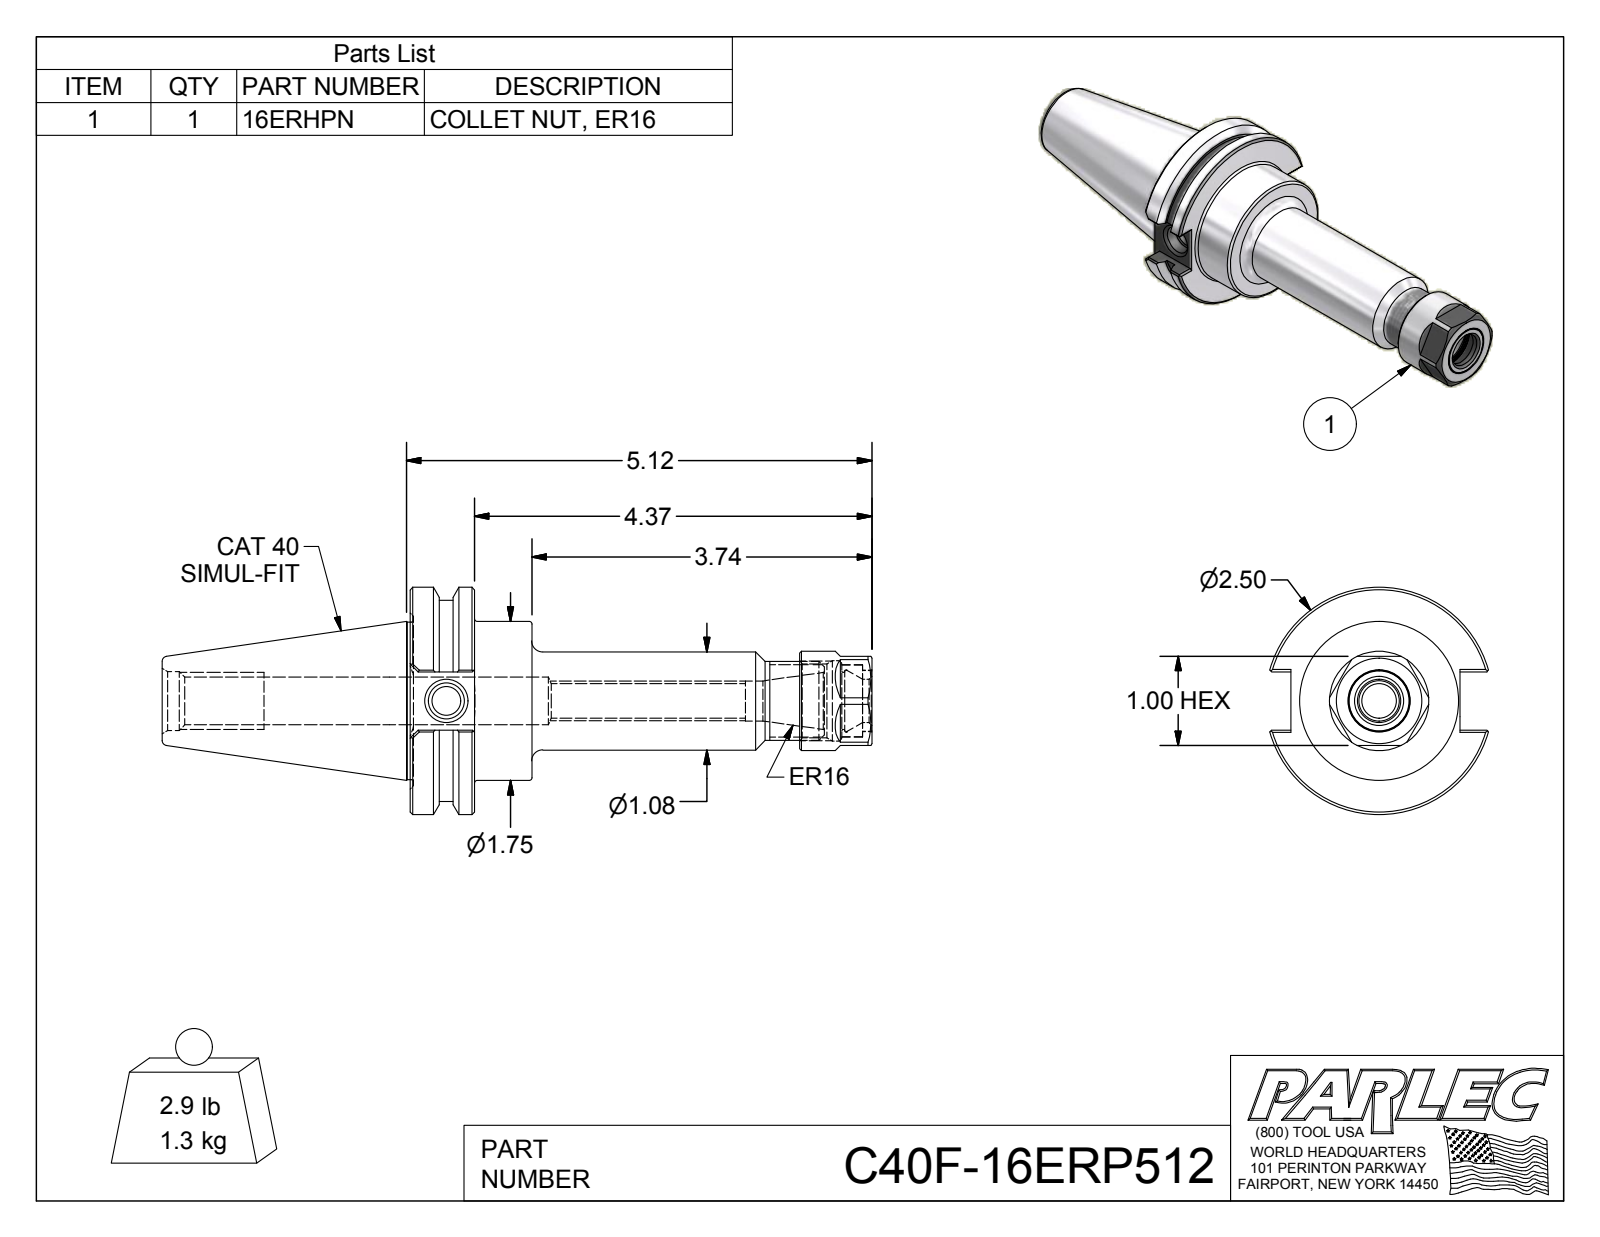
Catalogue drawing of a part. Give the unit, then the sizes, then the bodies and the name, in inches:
Units: inches
Overall size (bounding box): 7.808 × 2.5 × 2.406
Round holes (diameter × count): ⌀0.315 ×1, ⌀0.383 ×1, ⌀0.399 ×1, ⌀0.44 ×1, ⌀0.474 ×1, ⌀0.527 ×1, ⌀0.527 ×1, ⌀0.63 ×1, ⌀0.648 ×1, ⌀0.674 ×1, ⌀0.68 ×1, ⌀0.794 ×1
Round bosses / shafts (diameter × count): ⌀2.5 ×1, ⌀2.215 ×1, ⌀1.75 ×1, ⌀1.73 ×1, ⌀1.092 ×1, ⌀1.08 ×1, ⌀0.866 ×1, ⌀0.79 ×1
Main face-to-face distances: 0.71, 1.34, 0.63, 0.98, 5.08, 4.37, 3.74, 0.17, 0.81, 1.86
Volume: 10.27 in³ · Surface area: 58.15 in²
Bodies: 3 solids, 124 faces (54 planar, 27 cylindrical, 43 other)
Part name (STEP PRODUCT): C40F-16ERP512; C40F-16ER5-1; 16ERHPN
STEP written by: Autodesk Inventor 2012 (AUTOMOTIVE_DESIGN)
